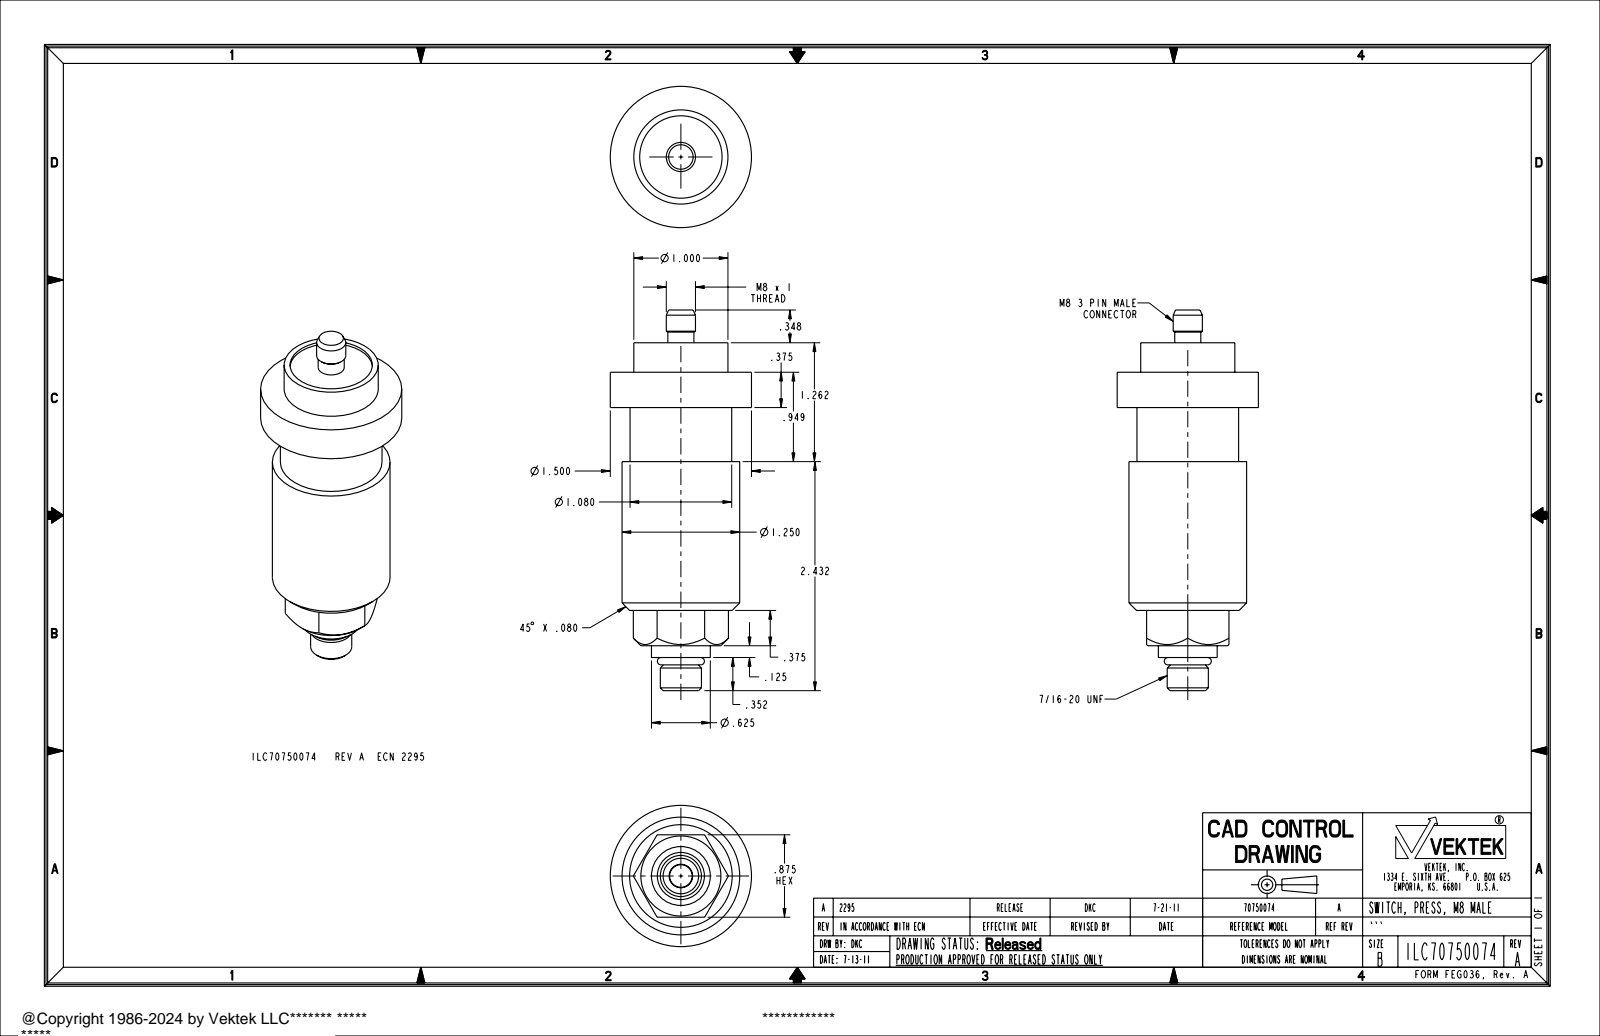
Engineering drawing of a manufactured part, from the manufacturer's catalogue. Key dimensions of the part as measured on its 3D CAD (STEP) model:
Part name (STEP PRODUCT): ILC70750074
STEP written by: PRO/ENGINEER BY PARAMETRIC TECHNOLOGY CORPORATION, 2007460 (AUTOMOTIVE_DESIGN_CC2)
Units: inches
Bodies: 1 solid, 59 faces (19 planar, 26 cylindrical, 14 other)
Overall size (bounding box): 4.042 × 1.5 × 1.5
Volume: 3.706 in³ · Surface area: 17.52 in²
Round holes (diameter × count): ⌀0.25 ×1, ⌀0.875 ×1
Round bosses / shafts (diameter × count): ⌀1.5 ×1, ⌀1.25 ×1, ⌀1.08 ×1, ⌀1 ×1, ⌀0.625 ×1, ⌀0.437 ×1, ⌀0.364 ×1, ⌀0.31 ×1
Main face-to-face distances: 0.375, 0.657, 0.282, 2.529, 0.875, 0.574, 0.949, 1.231, 1.58, 2.154
